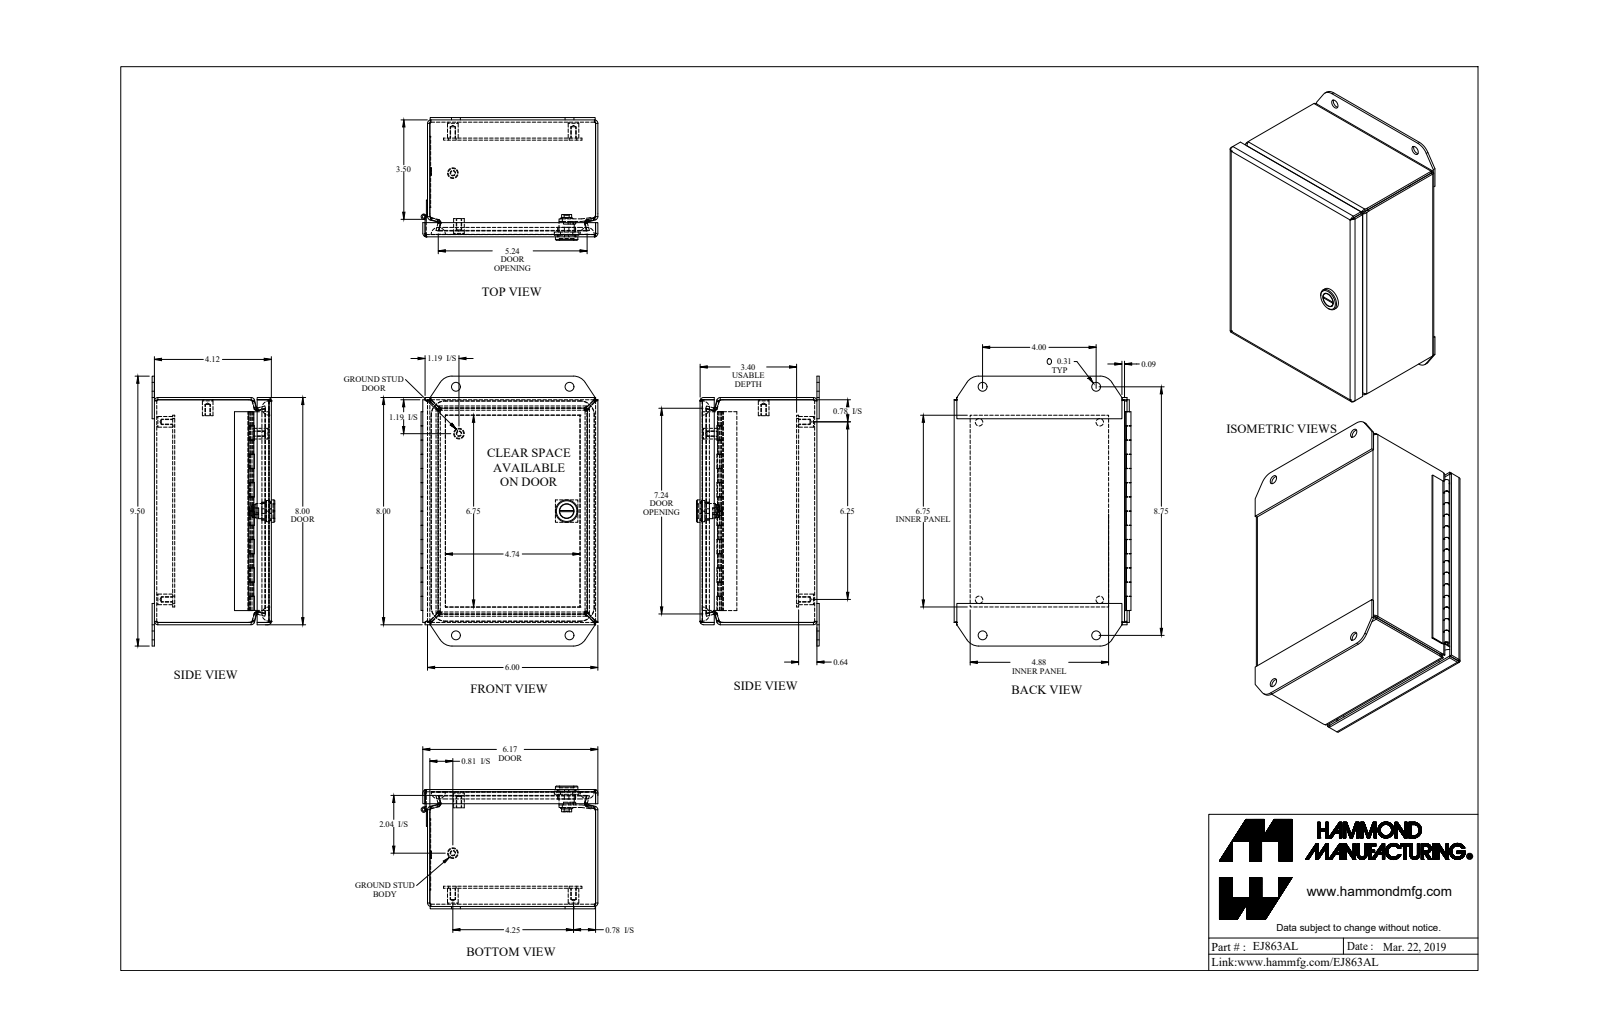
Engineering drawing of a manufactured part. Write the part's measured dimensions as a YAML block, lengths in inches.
part_name: "EJ863AL_Default"
step_written_by: "SolidWorks 2019 (CONFIG_CONTROL_DESIGN)"
units: inches
bodies: {solids: 14, faces: 586, planar: 364, cylindrical: 154, other: 68}
overall_size: [9.5, 6.226, 4.32]
volume: 24.67
surface_area: 631.5
round_holes:
  - {diameter: 0.159, count: 6}
  - {diameter: 0.265, count: 4}
  - {diameter: 0.313, count: 4}
  - {diameter: 0.516, count: 1}
round_bosses_or_shafts:
  - {diameter: 0.375, count: 6}
  - {diameter: 0.33, count: 6}
  - {diameter: 0.788, count: 1}
  - {diameter: 0.535, count: 1}
  - {diameter: 0.496, count: 1}
  - {diameter: 0.435, count: 1}
  - {diameter: 0.18, count: 1}
  - {diameter: 0.1, count: 1}
partial_cylinders:
  - {radius: 0.041, count: 16}
  - {radius: 0.121, count: 16}
  - {radius: 0.281, count: 12}
  - {radius: 0.25, count: 4}
  - {radius: 0.499, count: 4}
  - {radius: 0.5, count: 4}
  - {radius: 0.06, count: 2}
  - {radius: 0.03, count: 1}
face_to_face_distances: [0.081, 4.036, 4.117, 5.919, 3.955, 7.919, 0.643, 0.562, 3.474, 3.393]
hole_center_spacings: [0.024, 1.256, 4.25, 4.31, 7.502, 7.558, 8.56, 3.133]
